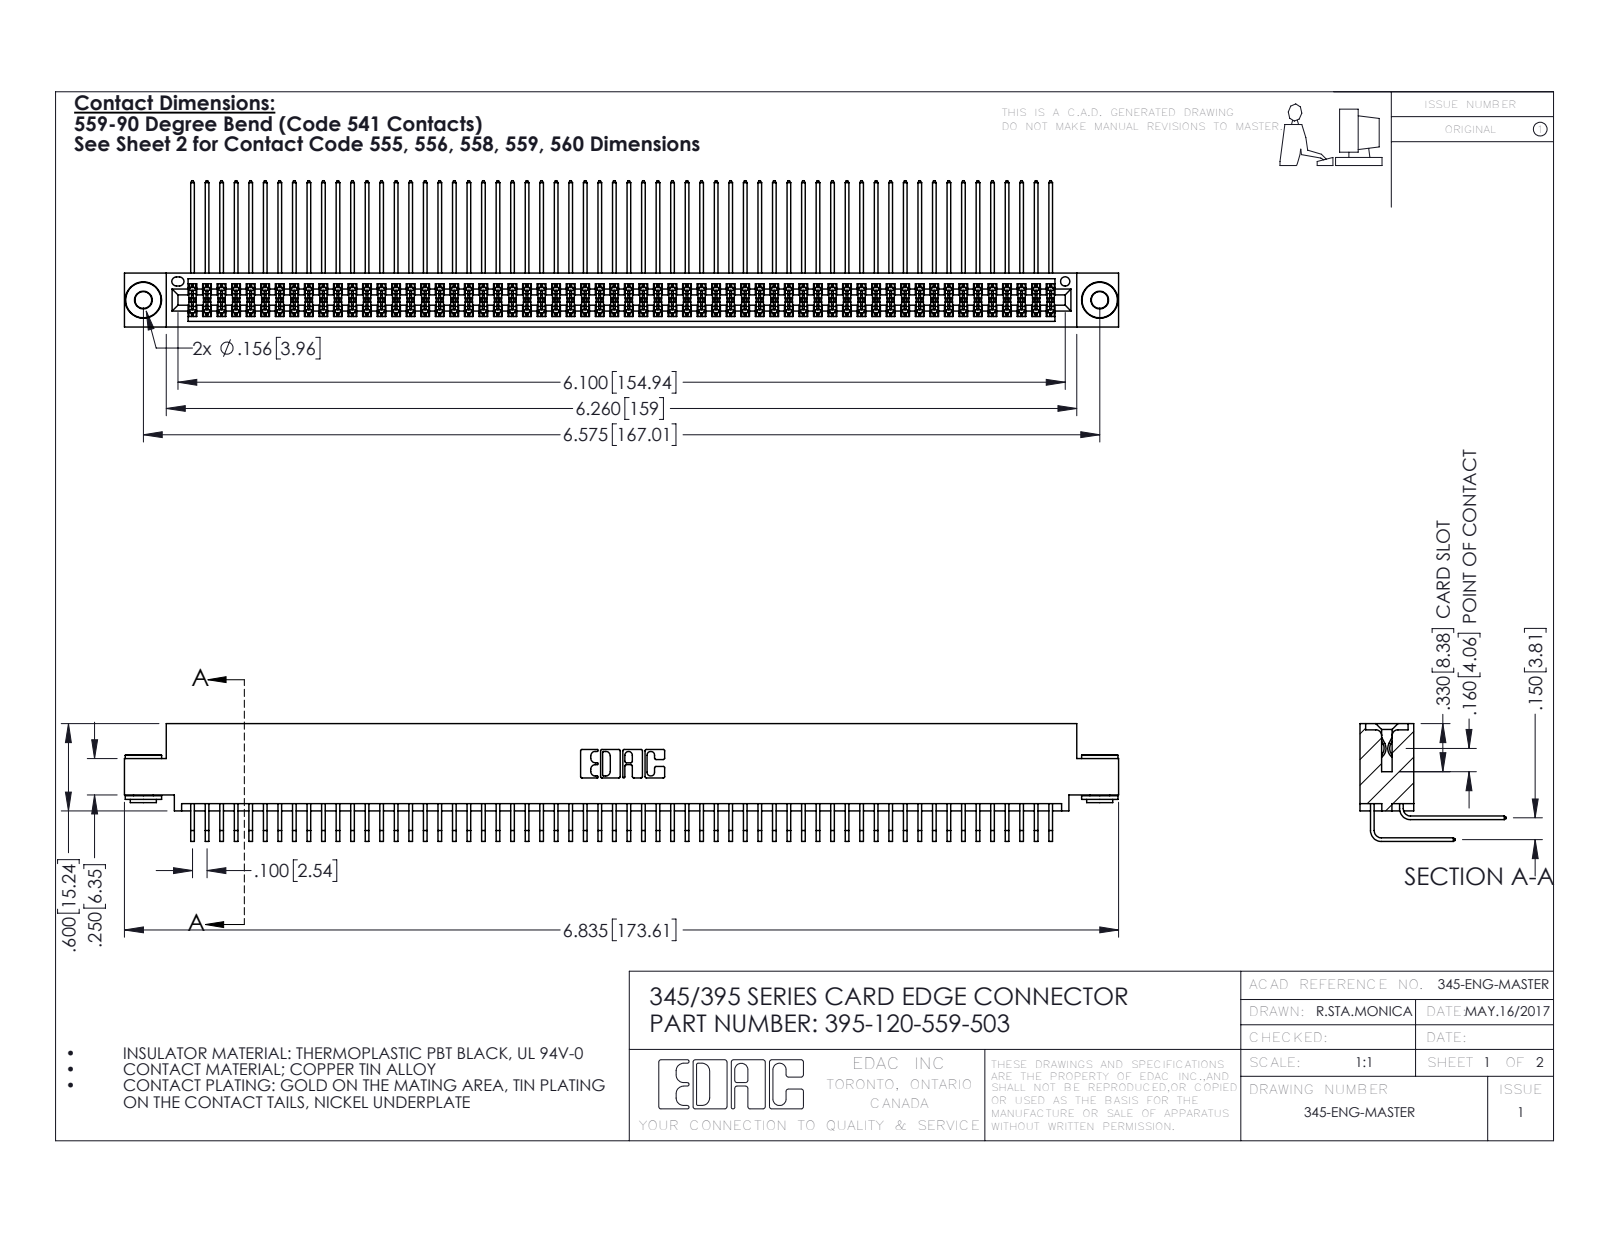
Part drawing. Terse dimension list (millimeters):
name: 345 Part_0.110 Offset - 0.156 Dia-TH; 345-292-001_559 Tail - 2; 345-292-001_558 559 Tail - 1; 345-250-002_345-250-002-102 (+1 more)
written by: SolidWorks 2016 (CONFIG_CONTROL_DESIGN)
unit: mm
bodies: 123 solids, 6408 faces (4294 planar, 2106 cylindrical, 8 other)
size: 173.6 × 25.5 × 20.5
volume: 17 670 mm³; area: 30 020 mm²
holes: 2× ⌀2.9, 2× ⌀4, 1× ⌀1.6
bosses: 2× ⌀6.4, 2× ⌀4.6, 2× ⌀3.5
rounds: 181× R0.2, 22× R0.3, 6× R0.2, 6× R0.8, 3× R0.7, 2× R0.4, 2× R0.5, 2× R0.6
face distances: 1.8, 7.6, 5.1, 9.4, 0.6, 2.5, 6.9, 5.7, 4.4, 3.8
hole spacings: 6.9, 161, 167
